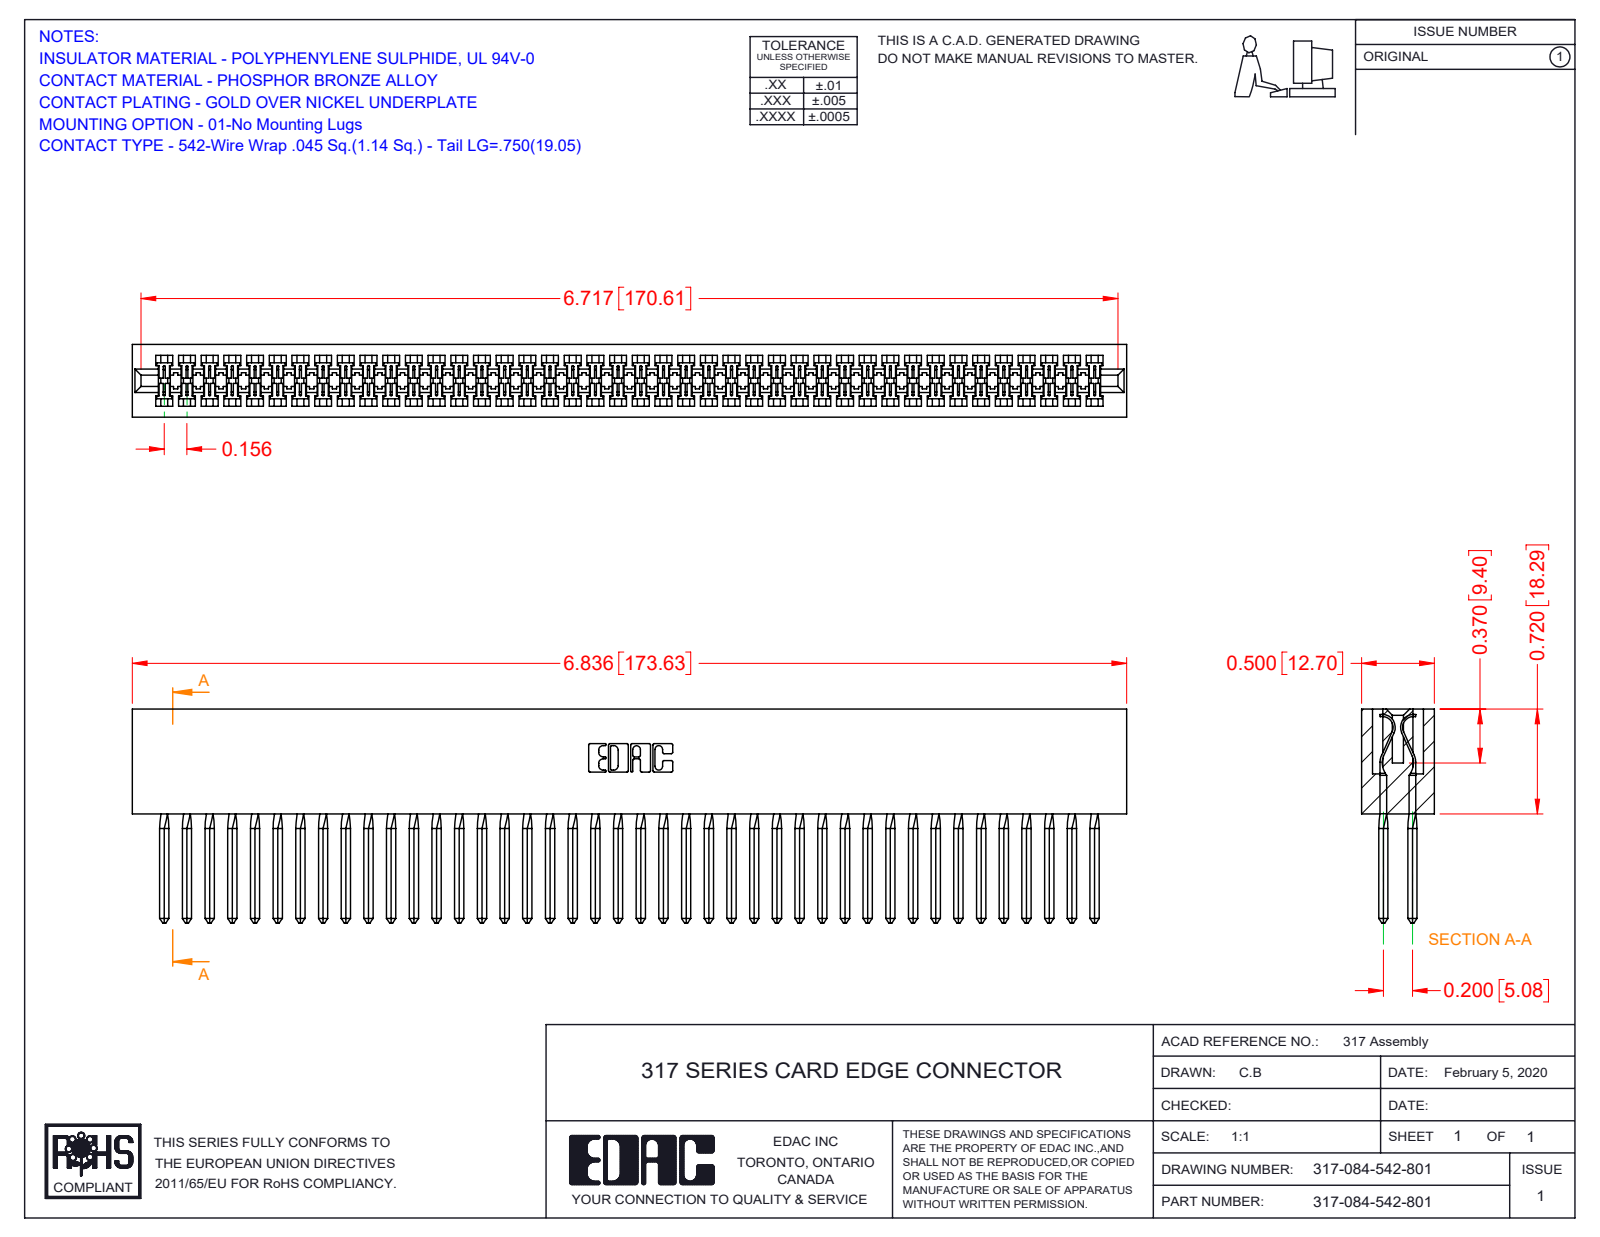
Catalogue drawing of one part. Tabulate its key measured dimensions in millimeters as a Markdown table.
| quantity | value |
| --- | --- |
| part name | 317-290-003_542; 317 Part_Lugless; 317-084-542-801 |
| STEP written by | SolidWorks 2016 (CONFIG_CONTROL_DESIGN) |
| units | millimeters |
| bodies | 85 solids, 4878 faces (3914 planar, 628 cylindrical, 336 other) |
| overall size | 173.6 × 37.3 × 12.7 |
| volume | 30 170 mm³ |
| surface area | 42 120 mm² |
| partial cylindrical surfaces (radius × count) | 0.2 × 168, 0.3 × 22, 0.2 × 6, 0.8 × 6, 0.7 × 3, 1.9 × 2, 2.3 × 2, 2.5 × 2 |
| main face-to-face distances | 1.9, 12.7, 10.8, 8.9, 5.1, 1.2, 3.3, 9.4, 1.3, 7.5 |
